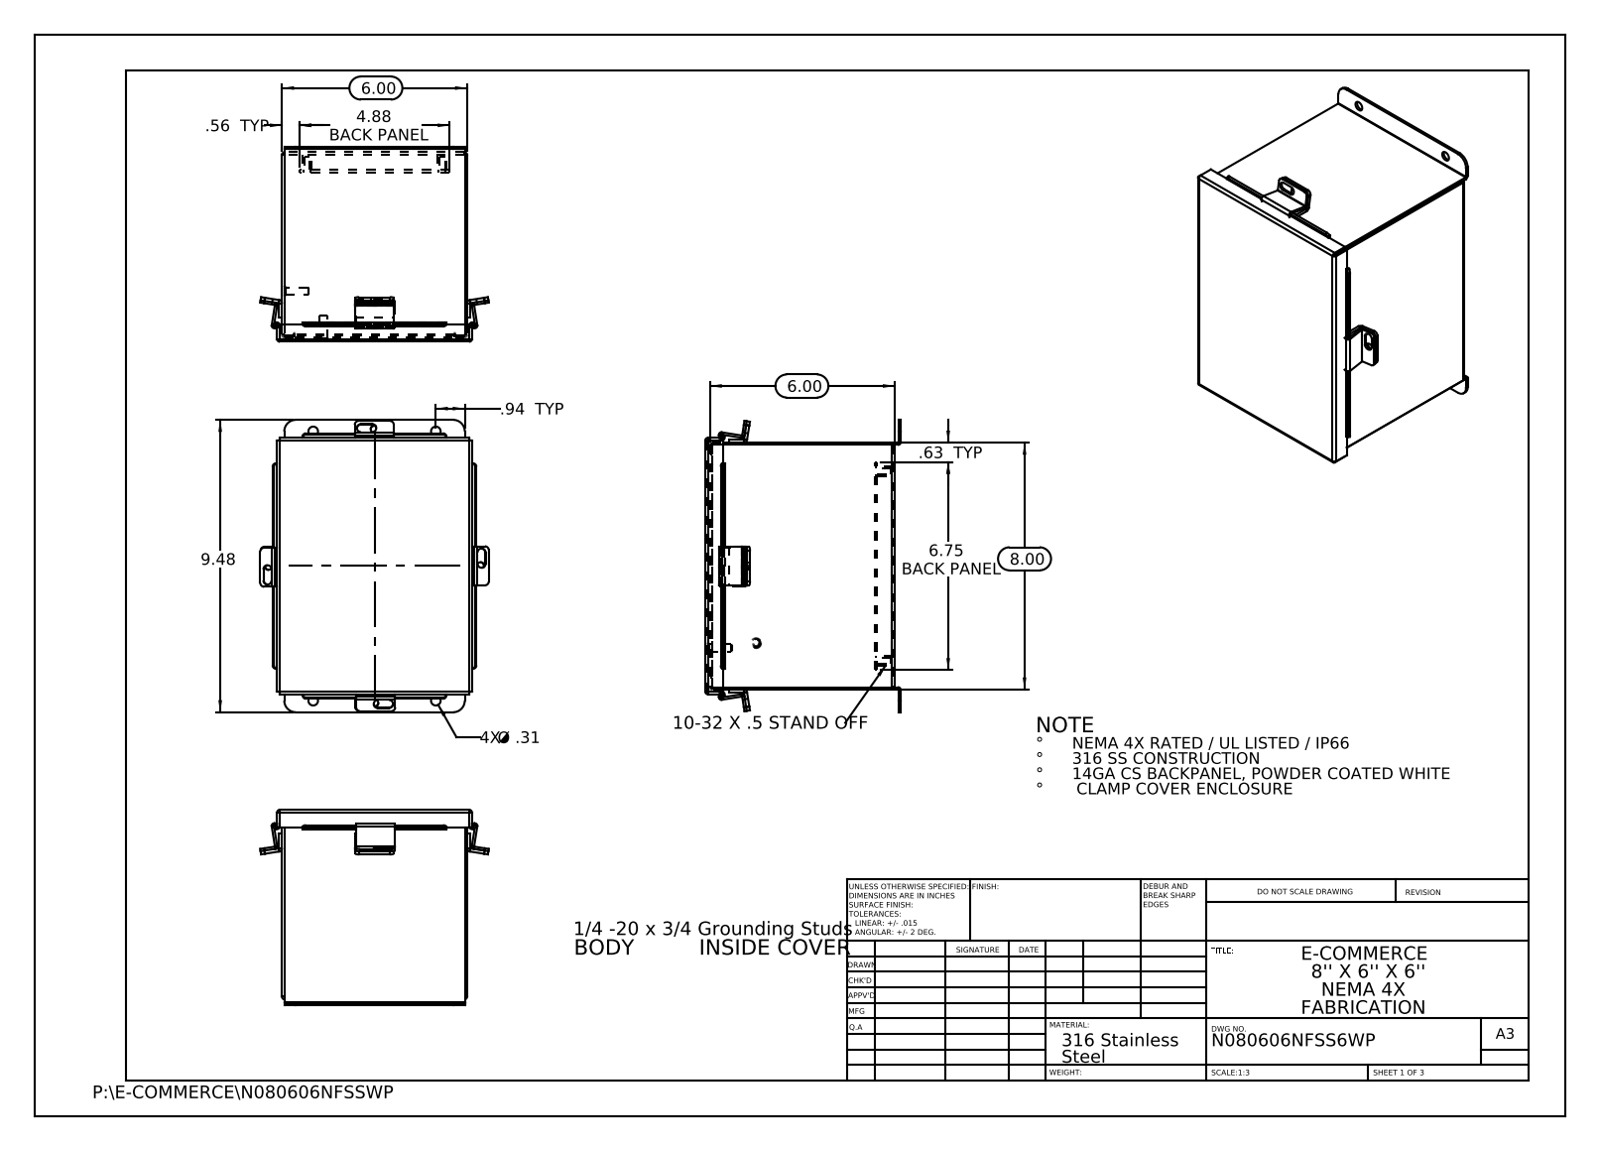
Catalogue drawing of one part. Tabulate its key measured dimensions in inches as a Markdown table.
| quantity | value |
| --- | --- |
| part name | N080606NFSSWP JIC_Standoff; N080606NFSSWP JIC Bottom; N080606NFSSWP JIC_Cover_Template; N080606NFSSWP JIC Top (+6 more) |
| STEP written by | SolidWorks 2013 (CONFIG_CONTROL_DESIGN) |
| units | inches |
| bodies | 19 solids, 456 faces (292 planar, 144 cylindrical, 20 other) |
| overall size | 9.476 × 7.407 × 6.39 |
| volume | 25.88 in³ |
| surface area | 706 in² |
| round holes (diameter × count) | 0.25 × 8, 0.187 × 4, 0.312 × 4 |
| round bosses / shafts (diameter × count) | 0.313 × 4, 0.315 × 2, 0.236 × 2 |
| partial cylindrical surfaces (radius × count) | 0.009 × 16, 0.125 × 14, 0.013 × 12, 0.088 × 12, 0.083 × 8, 0.1 × 8, 0.133 × 8, 0.084 × 4 |
| main face-to-face distances | 0.075, 5.925, 6.128, 7.925, 5.85, 6, 6.053, 6.203, 7.85, 8 |
| hole center spacings | 1.315, 4.373, 7.429, 8.519, 3.976, 4.375, 6.126, 7.528 |
